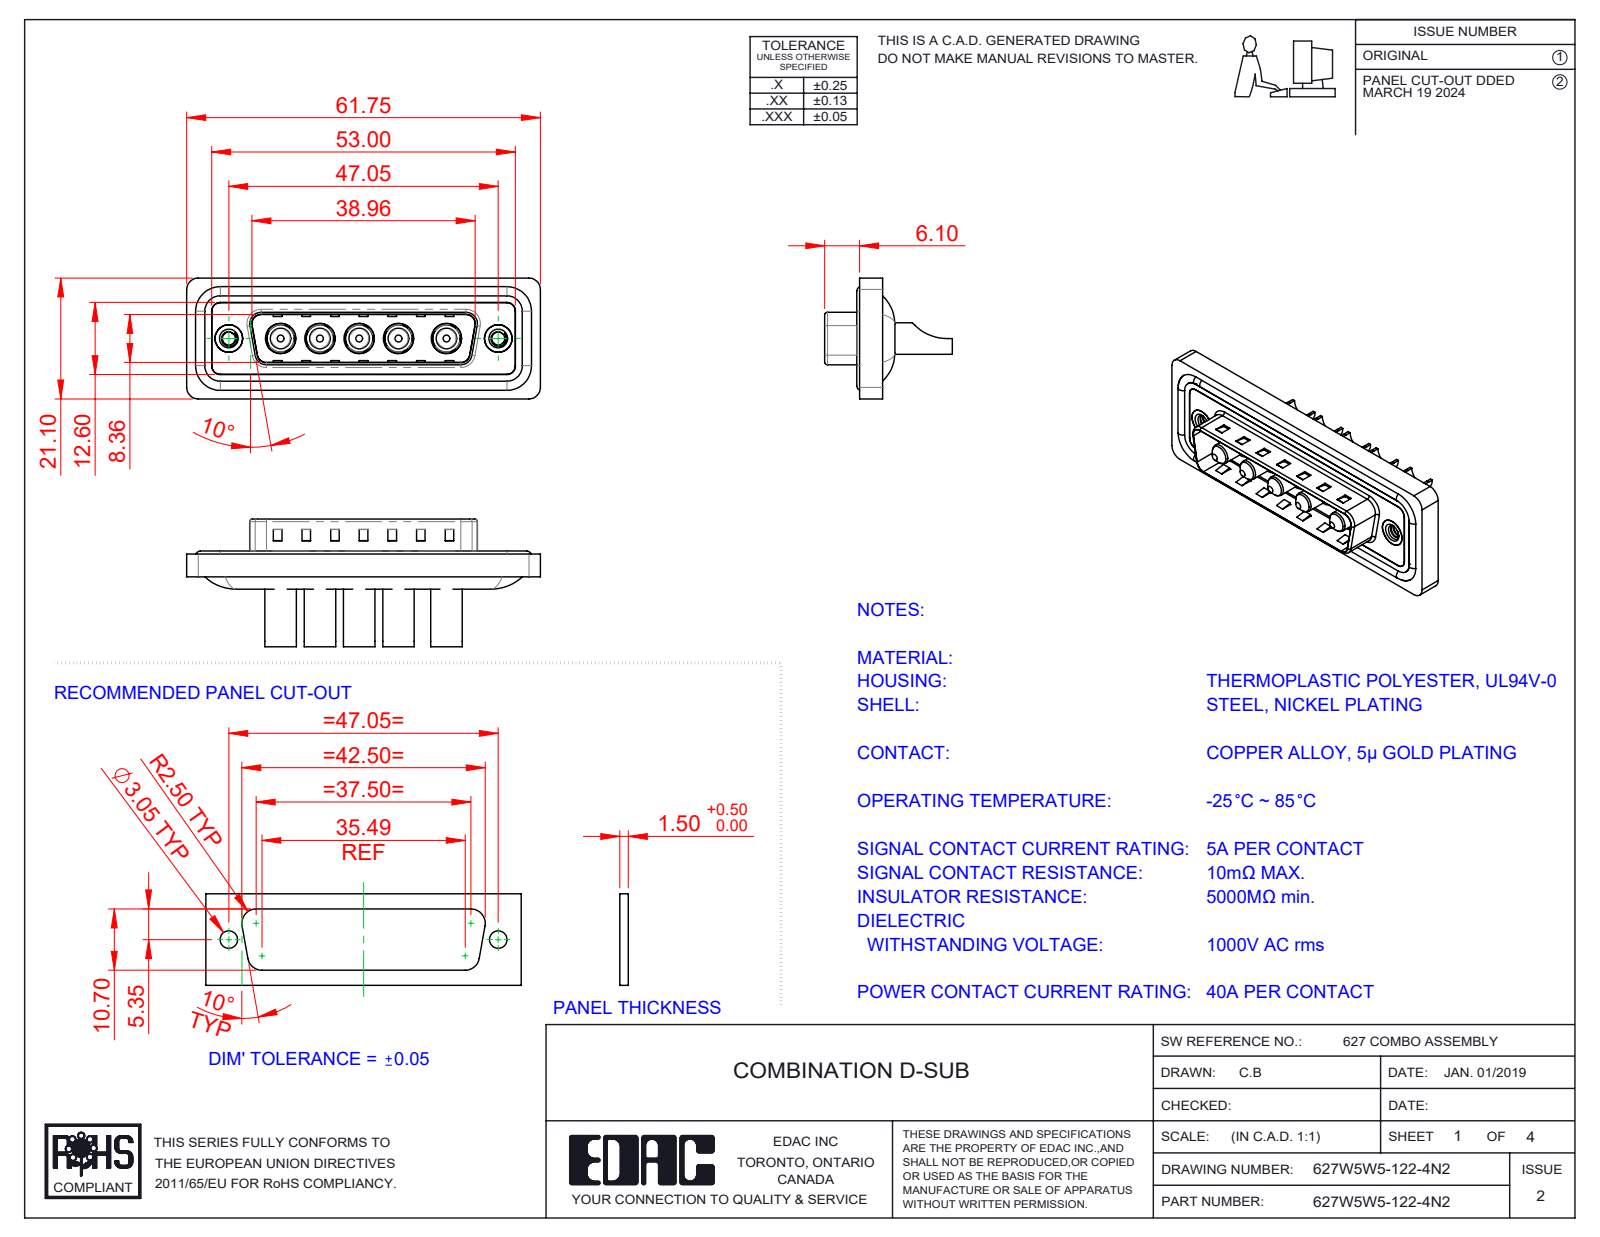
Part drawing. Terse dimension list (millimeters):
name: Power Pin_40A SC; 627Combo Shell Rear_25 Contacts; 627Combo Threaded Rivet_2; 627Combo Waterproof Housing_25 Contacts (+3 more)
written by: SolidWorks 2023 (CONFIG_CONTROL_DESIGN)
unit: mm
bodies: 17 solids, 693 faces (269 planar, 288 cylindrical, 136 other)
size: 61.75 × 22.3 × 21.1
volume: 7 672 mm³; area: 12 496 mm²
holes: 5× ⌀4.6, 5× ⌀4.85, 5× ⌀5.3, 2× ⌀2.26, 2× ⌀4, 2× ⌀4.8, 2× ⌀5
bosses: 5× ⌀5.5, 5× ⌀5.2, 5× ⌀4.75, 5× ⌀3.75, 5× ⌀3.6, 4× ⌀1.6, 2× ⌀4.9
rounds: 22× R1.5, 18× R2, 8× R0.5, 8× R1.6, 5× R2.1, 4× R0.25, 4× R0.6, 4× R0.65
face distances: 0.4, 0.5, 1.1, 1.5, 3.1, 1.6, 2.9, 0.82, 9.58, 5.65
hole spacings: 6.86, 9.04, 13.73, 38.01, 6.87, 8.37, 8.38, 9.05
